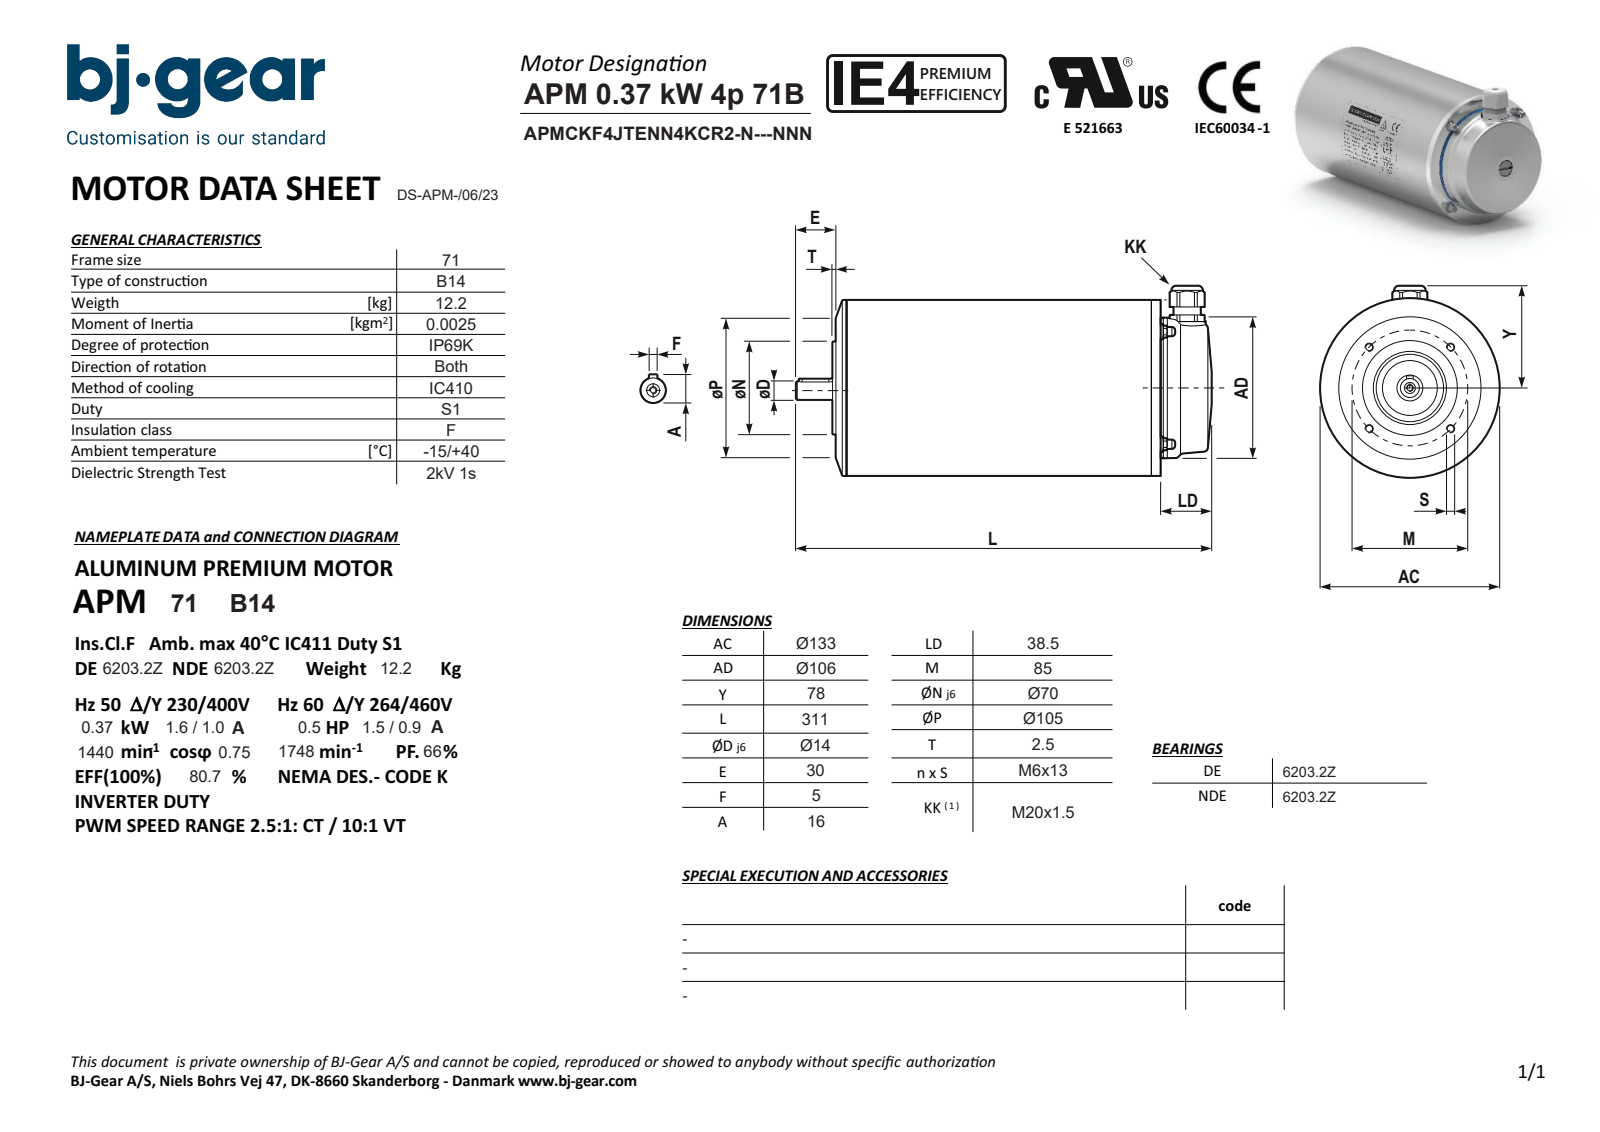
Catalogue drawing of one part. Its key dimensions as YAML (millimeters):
part_name: "APMCKF4JTENN4KCR2-N---NNN"
step_written_by: "Solid Edge (AUTOMOTIVE_DESIGN)"
units: millimeters
bodies: {solids: 1, faces: 156, planar: 71, cylindrical: 50, other: 35}
overall_size: [311, 143.3, 132.6]
volume: 3639000
surface_area: 145190
round_holes:
  - {diameter: 4.92, count: 4}
  - {diameter: 4.13, count: 1}
  - {diameter: 5.3, count: 1}
  - {diameter: 16, count: 1}
  - {diameter: 28, count: 1}
  - {diameter: 52, count: 1}
round_bosses_or_shafts:
  - {diameter: 11.5, count: 4}
  - {diameter: 7, count: 4}
  - {diameter: 132.6, count: 1}
  - {diameter: 132.6, count: 1}
  - {diameter: 106, count: 1}
  - {diameter: 70, count: 1}
  - {diameter: 23.7, count: 1}
  - {diameter: 20.6, count: 1}
partial_cylinders:
  - {radius: 2.5, count: 2}
  - {radius: 13.2, count: 1}
face_to_face_distances: [242.5, 237, 5.5, 8, 2.5, 245, 283.5, 38.5, 275.5, 281]
hole_center_spacings: [42.5, 60.1, 84.99]
